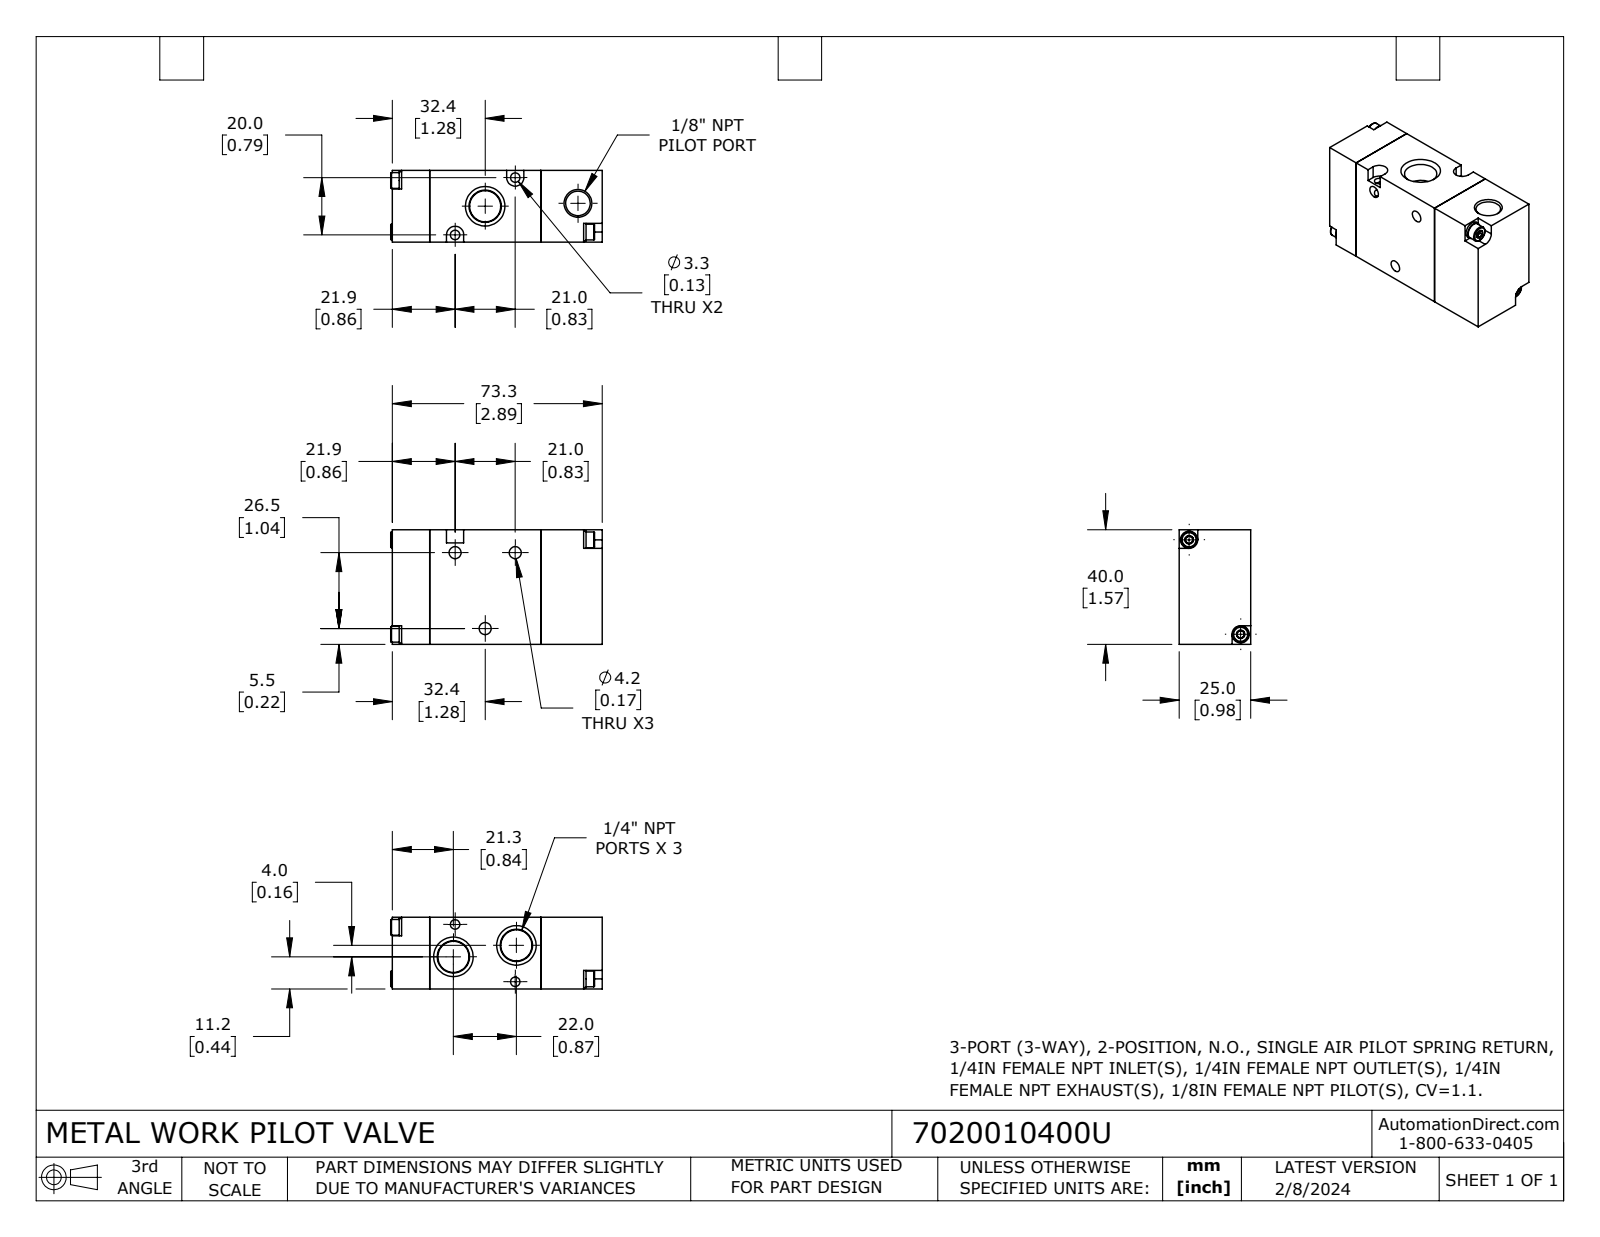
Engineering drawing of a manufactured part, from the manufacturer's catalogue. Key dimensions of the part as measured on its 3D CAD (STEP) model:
Part name (STEP PRODUCT): 7020010400U
STEP written by: SolidWorks 2023 (CONFIG_CONTROL_DESIGN)
Units: inches
Bodies: 11 solids, 233 faces (108 planar, 55 cylindrical, 70 other)
Overall size (bounding box): 2.909 × 1.575 × 0.984
Volume: 4.179 in³ · Surface area: 29.68 in²
Round holes (diameter × count): ⌀0.118 ×4, ⌀0.165 ×3, ⌀0.13 ×2, ⌀0.337 ×1
Round bosses / shafts (diameter × count): ⌀0.236 ×4, ⌀0.217 ×4
Partial cylindrical surfaces — rounded edges, fillets, slot ends (radius × count): R0.118 ×2
Main face-to-face distances: 0.984, 1.528, 1.575, 2.374, 0.846, 0.512, 2.039, 2.886, 0.311, 1.264
Hole centre spacings: 0.709, 1.122, 1.299, 1.48, 0.827, 0.932, 1.142, 1.744
